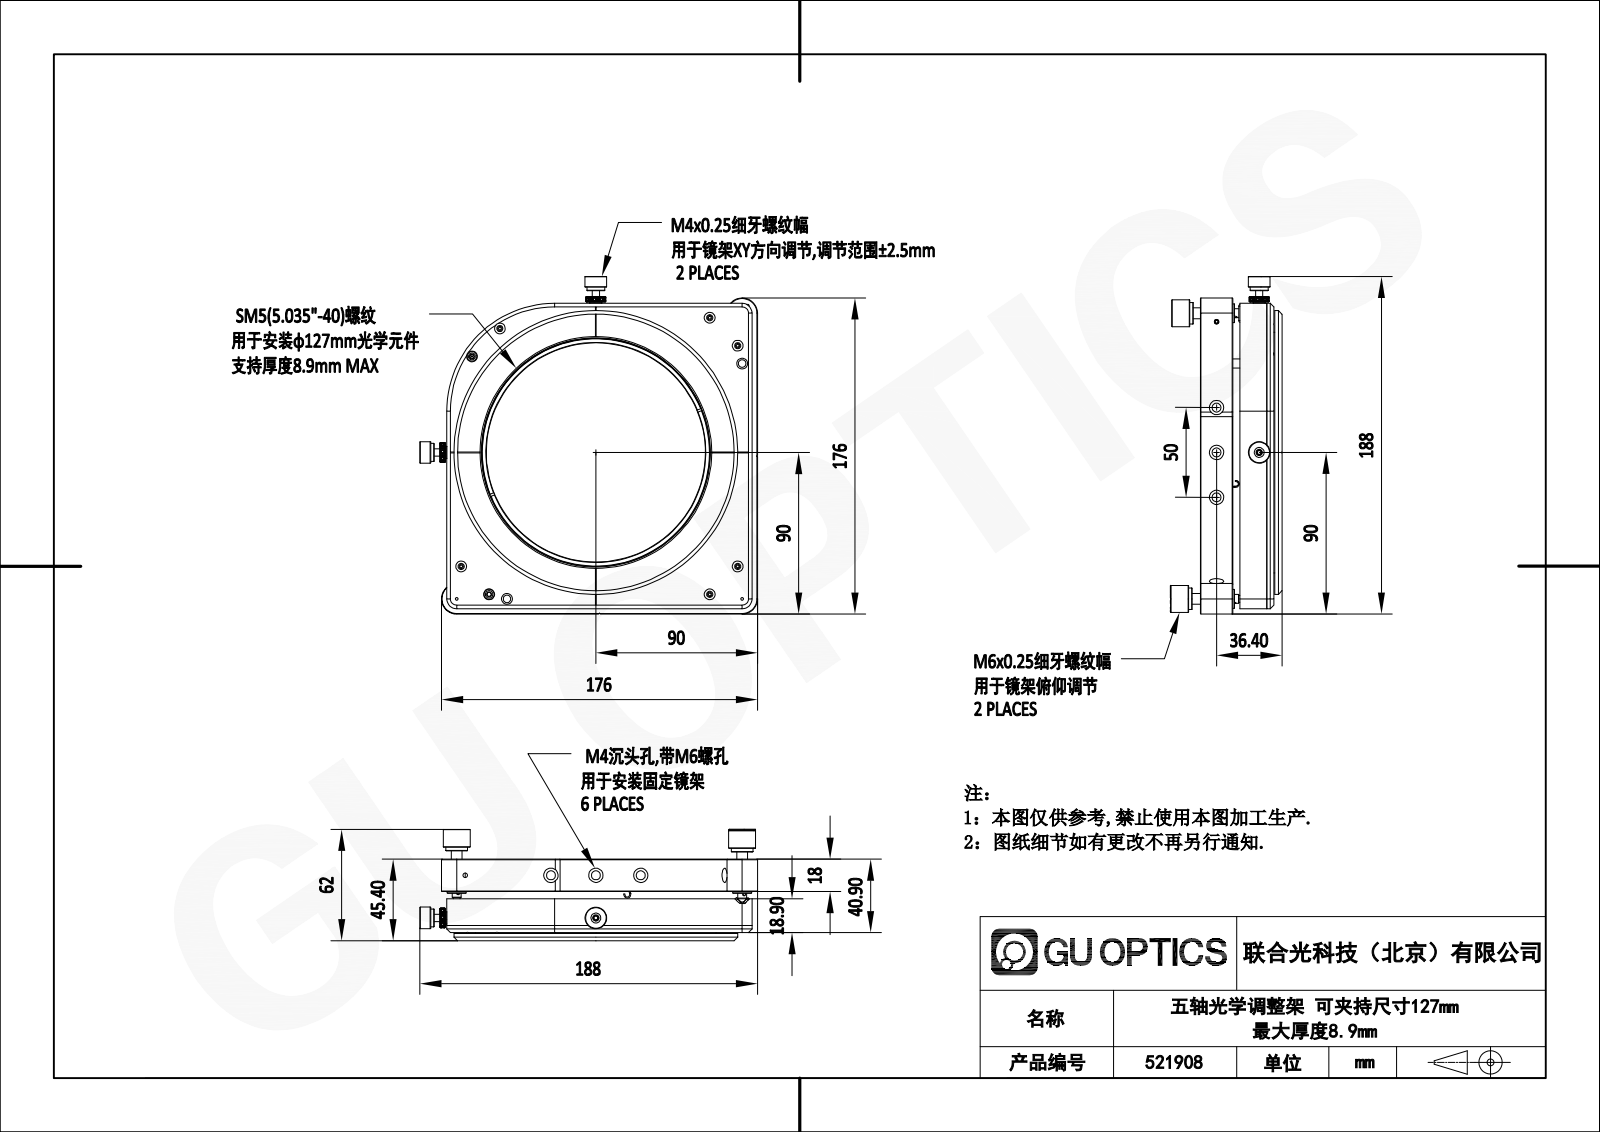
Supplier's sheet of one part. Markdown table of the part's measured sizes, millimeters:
| quantity | value |
| --- | --- |
| part name | 521908 |
| STEP written by | SolidWorks 2020 (CONFIG_CONTROL_DESIGN) |
| units | millimeters |
| bodies | 0 solids, 975 faces (494 planar, 269 cylindrical, 212 other) |
| overall size | 188 × 188 × 62.08 |
| round holes (diameter × count) | 5 × 6, 6.5 × 6, 8 × 6, 9.5 × 3, 10.5 × 3, 1.8 × 2, 3.5 × 2, 11 × 2, 2.5 × 1, 5.5 × 1, 122 × 1, 129 × 1 |
| round bosses / shafts (diameter × count) | 6 × 13, 1.5 × 10, 3.4 × 6, 5 × 4, 2.5 × 4, 15 × 3, 12 × 2, 10 × 2 |
| partial cylindrical surfaces (radius × count) | 1.05 × 12, 5.5 × 5, 5 × 4, 1 × 3, 8.5 × 3, 10 × 2, 60 × 1, 76 × 1 |
| main face-to-face distances | 15, 18.9, 3.9, 12.4, 19, 4, 18, 22.9, 4.5, 10.5 |
| hole center spacings | 25, 34.48, 50, 17, 23.75, 24, 28, 40 |
